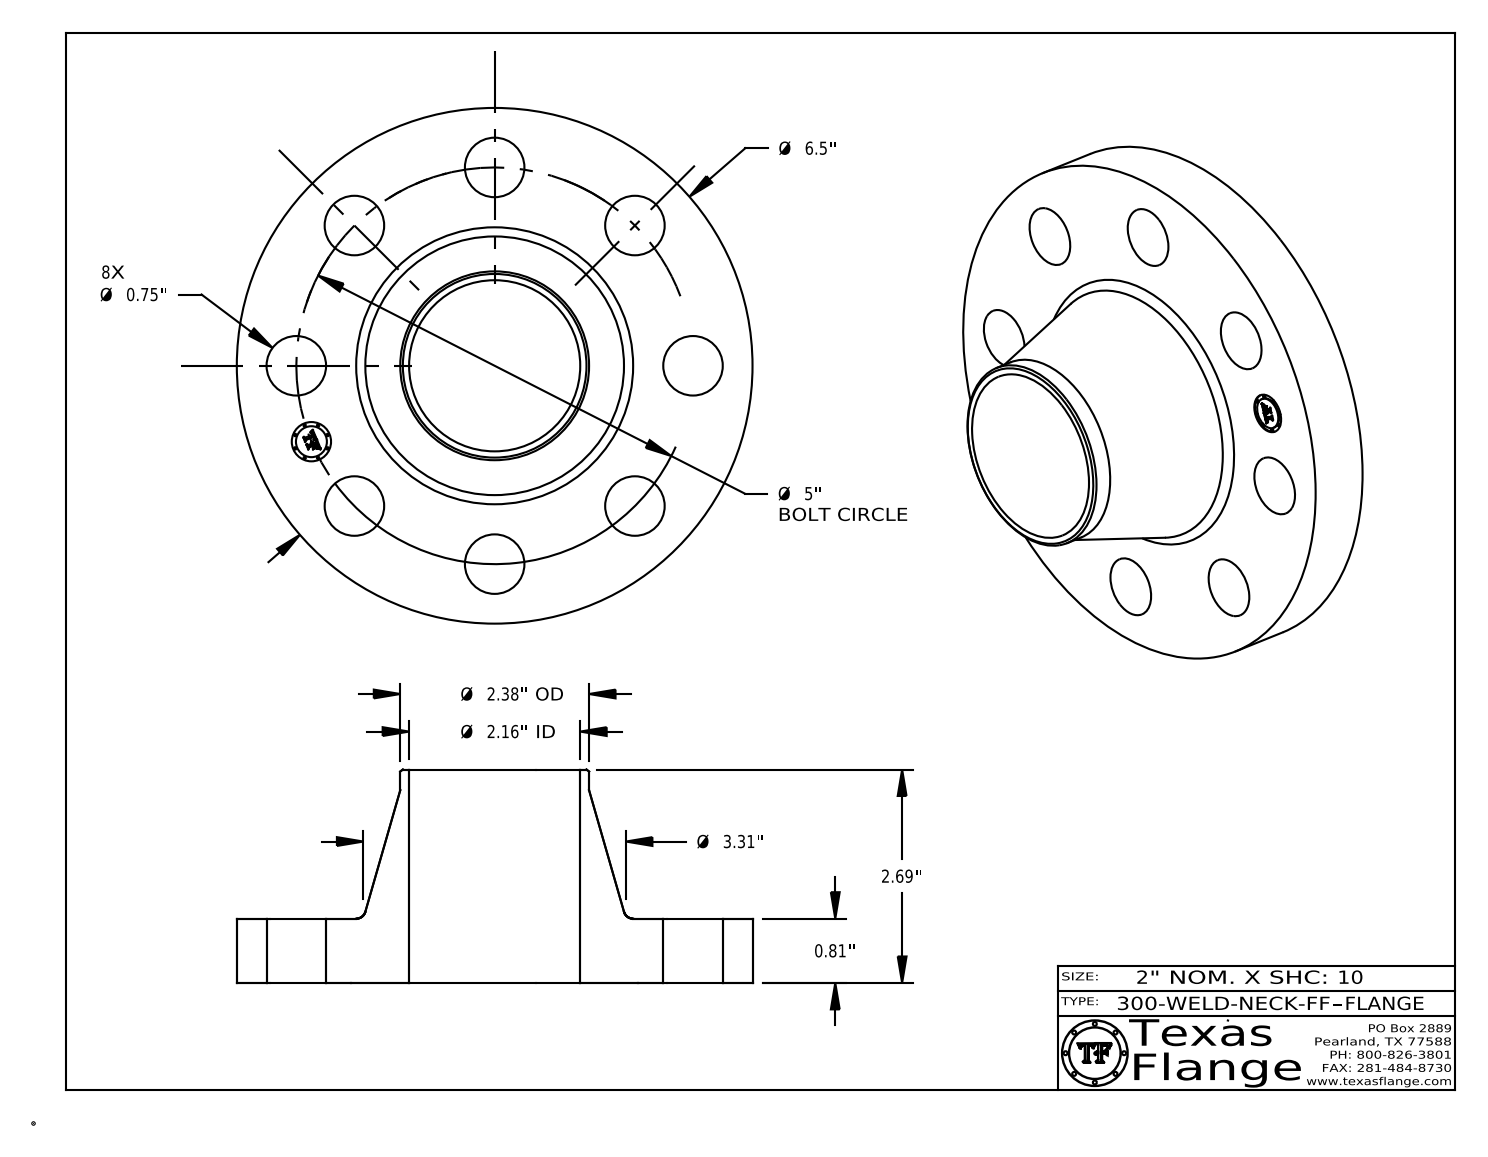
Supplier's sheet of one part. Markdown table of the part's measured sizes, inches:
| quantity | value |
| --- | --- |
| part name | 300-WELD-NECK-FF |
| STEP written by | CATIA V5 STEP AP214 (AUTOMOTIVE_DESIGN) |
| units | inches |
| bodies | 1 solid, 417 faces (369 planar, 42 cylindrical, 6 other) |
| overall size | 6.5 × 6.5 × 2.69 |
| volume | 25.74 in³ |
| surface area | 114.6 in² |
| round holes (diameter × count) | 0.75 × 8, 0.495 × 1, 2.157 × 1 |
| round bosses / shafts (diameter × count) | 0.03 × 8, 6.5 × 1, 2.38 × 1, 0.39 × 1 |
| main face-to-face distances | 0.81, 2.69, 1.88, 0.795, 0.015, 1.895, 0.148, 0.145, 0.027, 0.096 |
| hole center spacings | 2.5, 1.913, 3.535, 4.619, 5, 0.976, 2.778, 4.157 |
